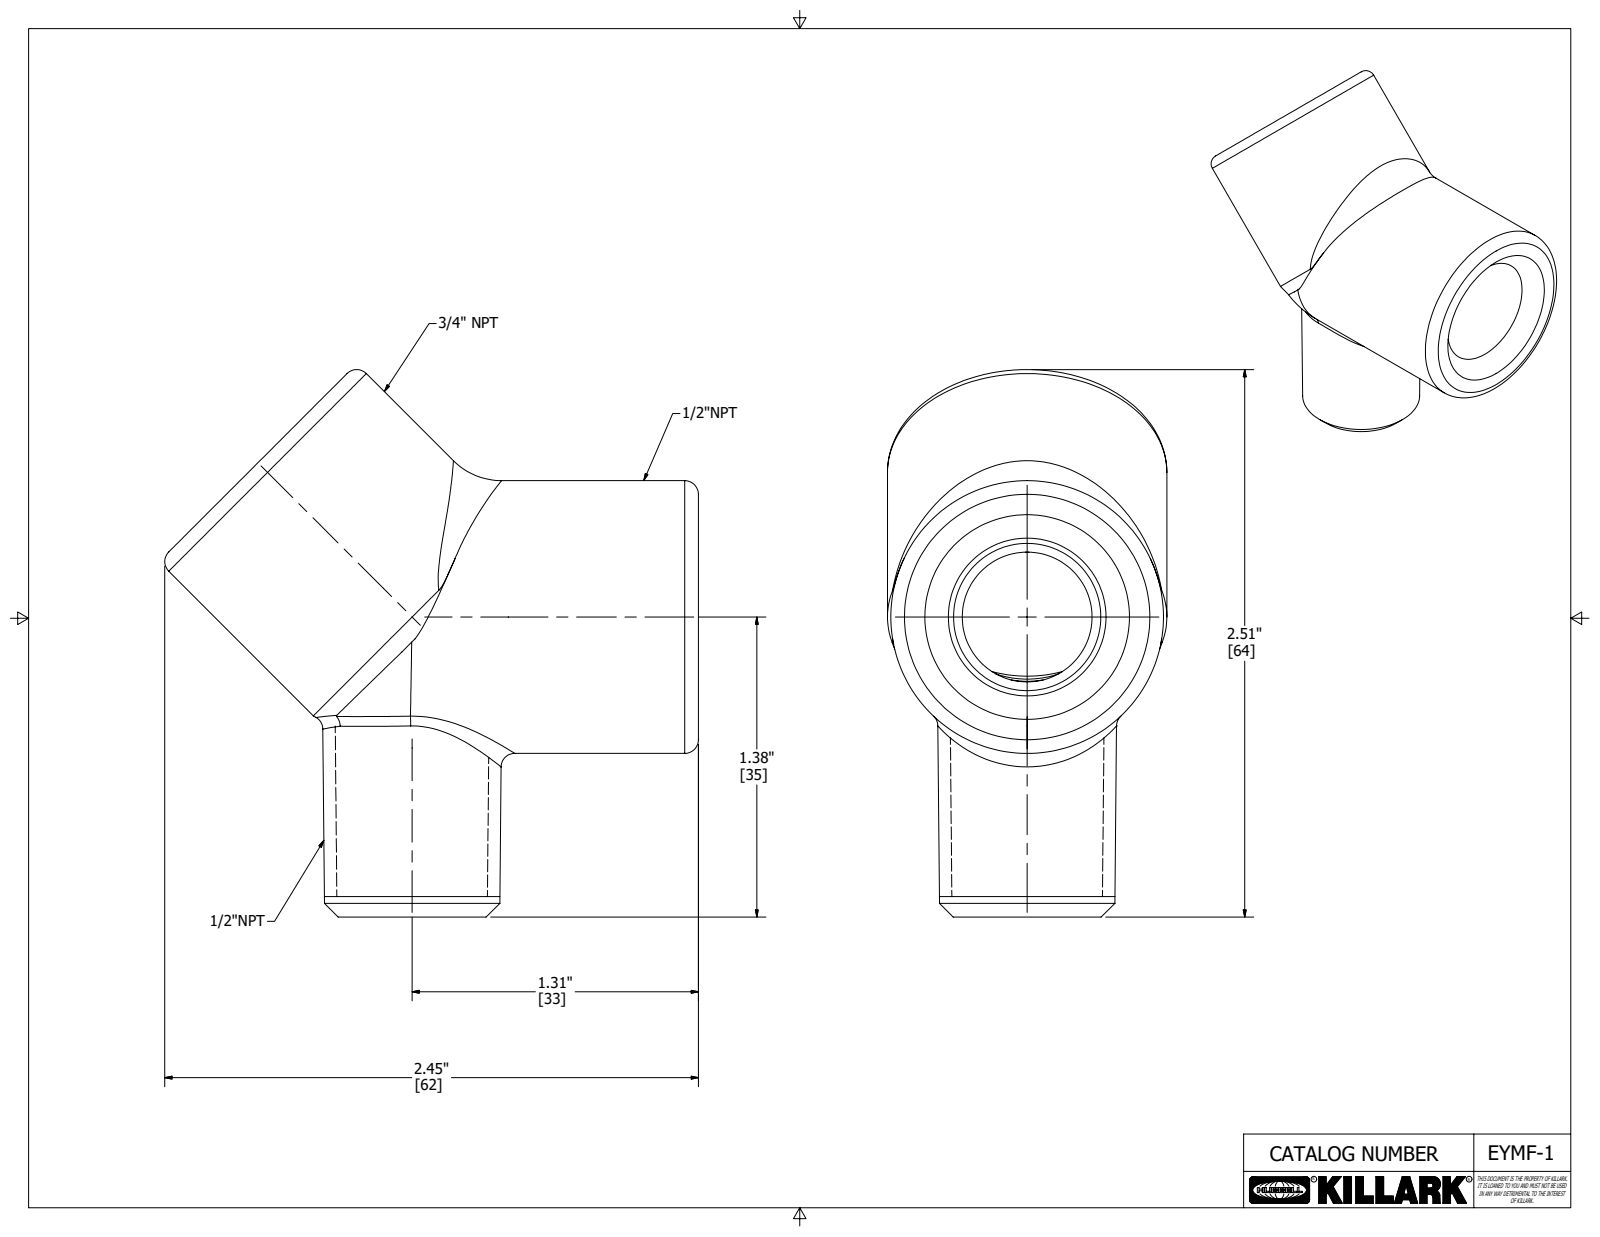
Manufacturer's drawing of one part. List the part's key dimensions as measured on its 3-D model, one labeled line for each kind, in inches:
Part name (STEP PRODUCT): 12691-2
STEP written by: Autodesk Inventor 2020 (AUTOMOTIVE_DESIGN)
Units: inches
Bodies: 1 solid, 75 faces (6 planar, 9 cylindrical, 60 other)
Overall size (bounding box): 2.509 × 2.447 × 1.281
Volume: 1.752 in³ · Surface area: 19.77 in²
Round holes (diameter × count): ⌀0.56 ×1, ⌀0.723 ×1, ⌀0.966 ×1
Round bosses / shafts (diameter × count): ⌀1.281 ×1, ⌀1.25 ×1, ⌀0.816 ×1
Partial cylindrical surfaces — rounded edges, fillets, slot ends (radius × count): R0.297 ×1, R0.471 ×1
Main face-to-face distances: 0.875, 0.156, 1.031, 1
